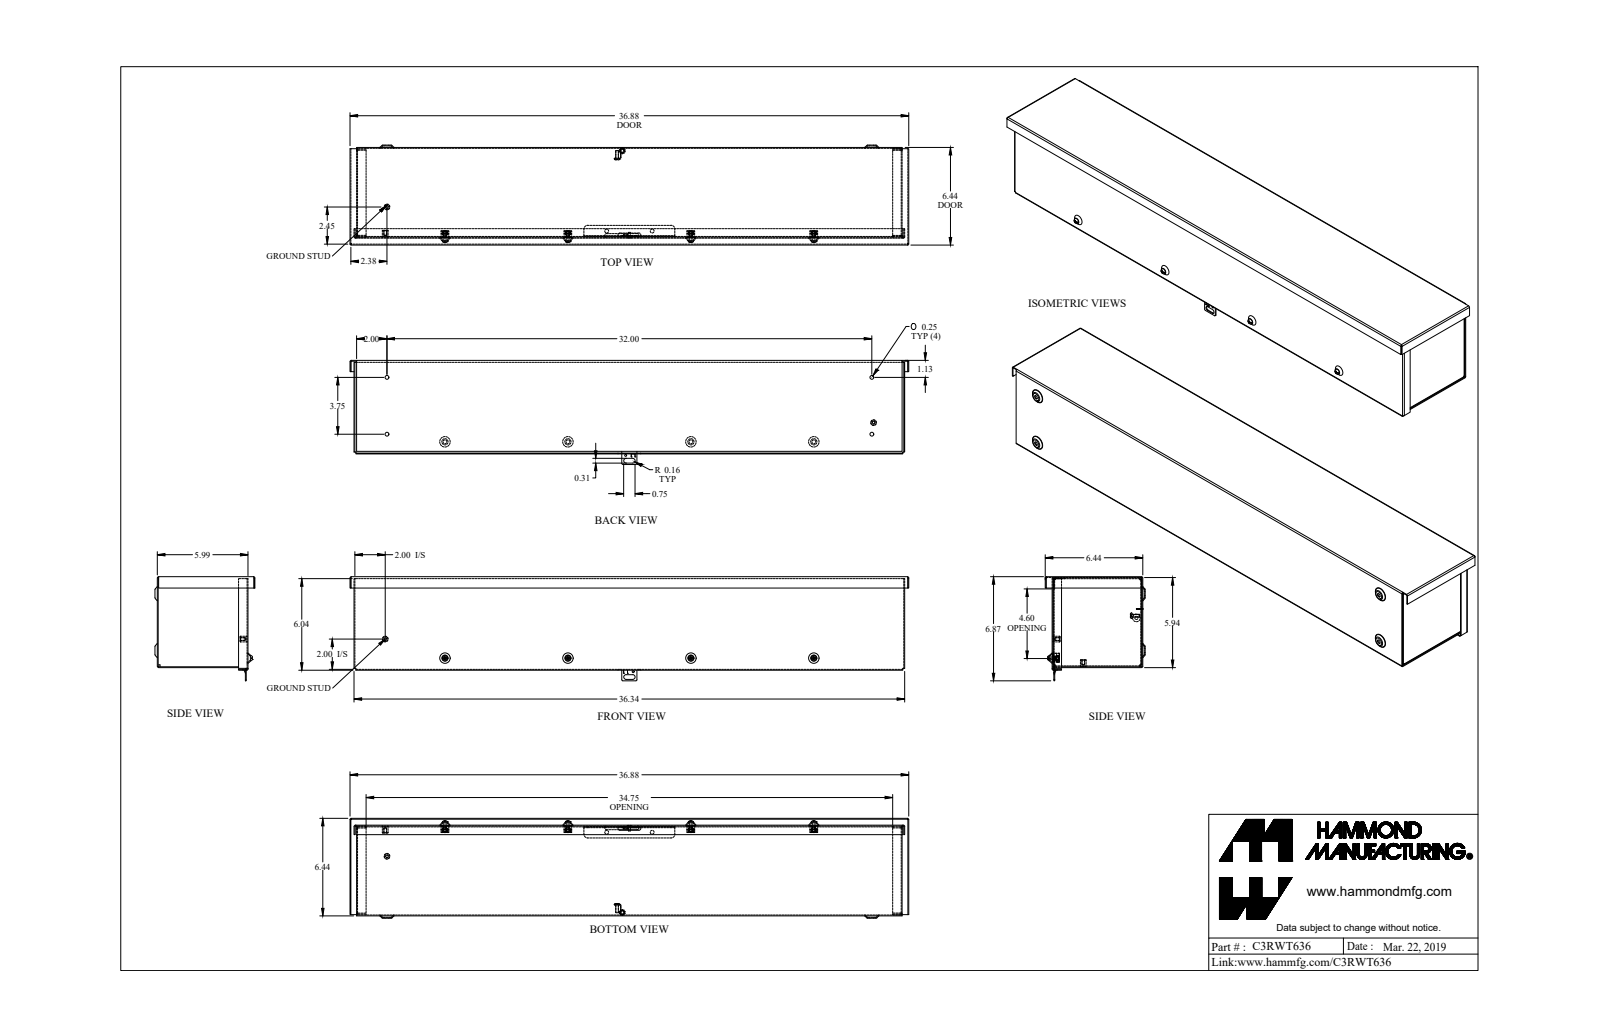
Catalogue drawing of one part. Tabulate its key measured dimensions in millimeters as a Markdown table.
| quantity | value |
| --- | --- |
| part name | C3RWT636_Default |
| STEP written by | SolidWorks 2019 (CONFIG_CONTROL_DESIGN) |
| units | millimeters |
| bodies | 25 solids, 887 faces (486 planar, 277 cylindrical, 124 other) |
| overall size | 936.6 × 174.5 × 167.5 |
| volume | 1 010 000 mm³ |
| surface area | 1 405 000 mm² |
| round holes (diameter × count) | 4 × 6, 6.4 × 6, 5.4 × 4, 5.8 × 4, 5.2 × 2, 3.2 × 1, 3.5 × 1, 5.1 × 1, 5.5 × 1 |
| round bosses / shafts (diameter × count) | 4.8 × 5, 3.8 × 4, 9.5 × 2, 12.7 × 1, 9.3 × 1, 5.3 × 1, 3.9 × 1, 3.2 × 1 |
| partial cylindrical surfaces (radius × count) | 0.7 × 18, 2.2 × 18, 2 × 16, 2.7 × 16, 3.2 × 14, 0.6 × 8, 6.4 × 6, 0.4 × 4 |
| main face-to-face distances | 1.4, 151, 150.6, 149.1, 149.5, 152, 152.4, 913, 4.4, 162.1 |
| hole center spacings | 206.1, 412.2, 103.1, 206.1, 245.2, 275.6, 303.6, 509.6 |
